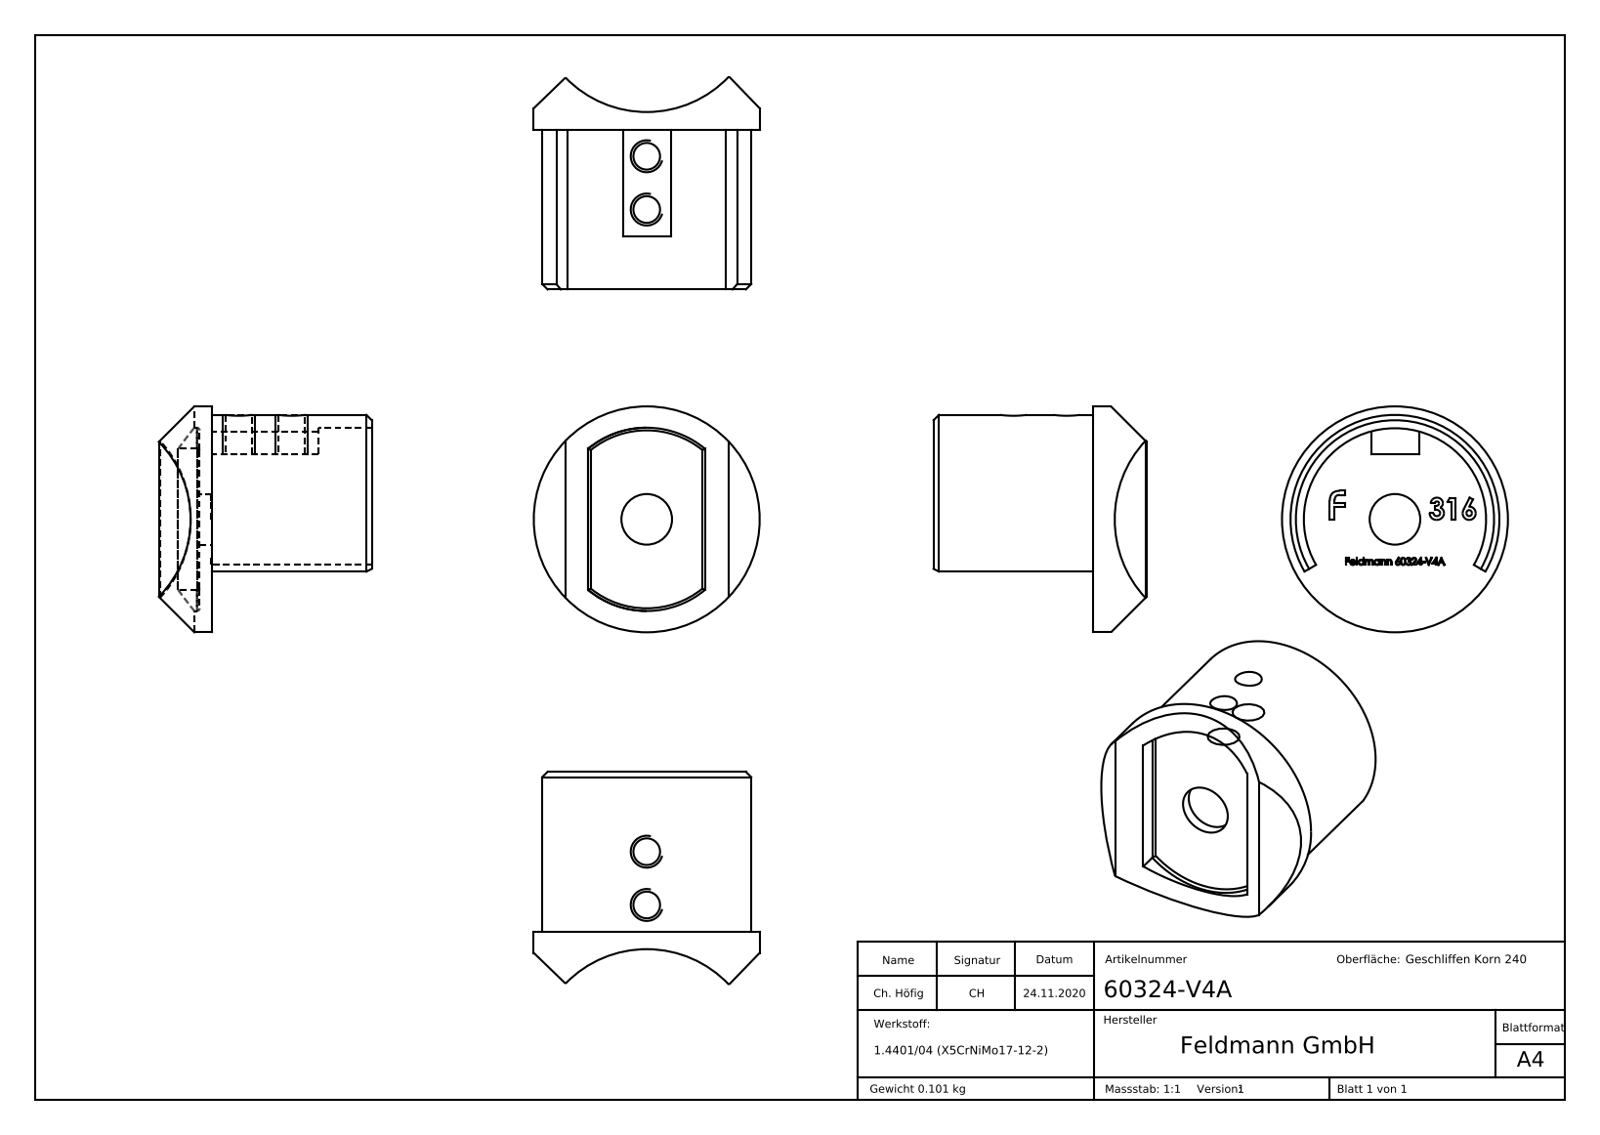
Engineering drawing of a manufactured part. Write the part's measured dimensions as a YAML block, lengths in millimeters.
part_name: "60324-V4A"
step_written_by: "SolidWorks 2018 (CONFIG_CONTROL_DESIGN)"
units: millimeters
bodies: {solids: 1, faces: 312, planar: 179, cylindrical: 19, other: 114}
overall_size: [42.4, 42.4, 39.97]
volume: 12589
surface_area: 9047
round_holes:
  - {diameter: 5, count: 2}
  - {diameter: 9.5, count: 1}
round_bosses_or_shafts:
  - {diameter: 42.4, count: 1}
partial_cylinders:
  - {radius: 0.5, count: 2}
  - {radius: 17.1, count: 1}
  - {radius: 17.2, count: 1}
  - {radius: 19.6, count: 1}
  - {radius: 21.2, count: 1}
face_to_face_distances: [2.3, 30, 32.3, 21.96, 9, 10, 20, 22.3, 2.2, 30.1]
hole_center_spacings: [10]
